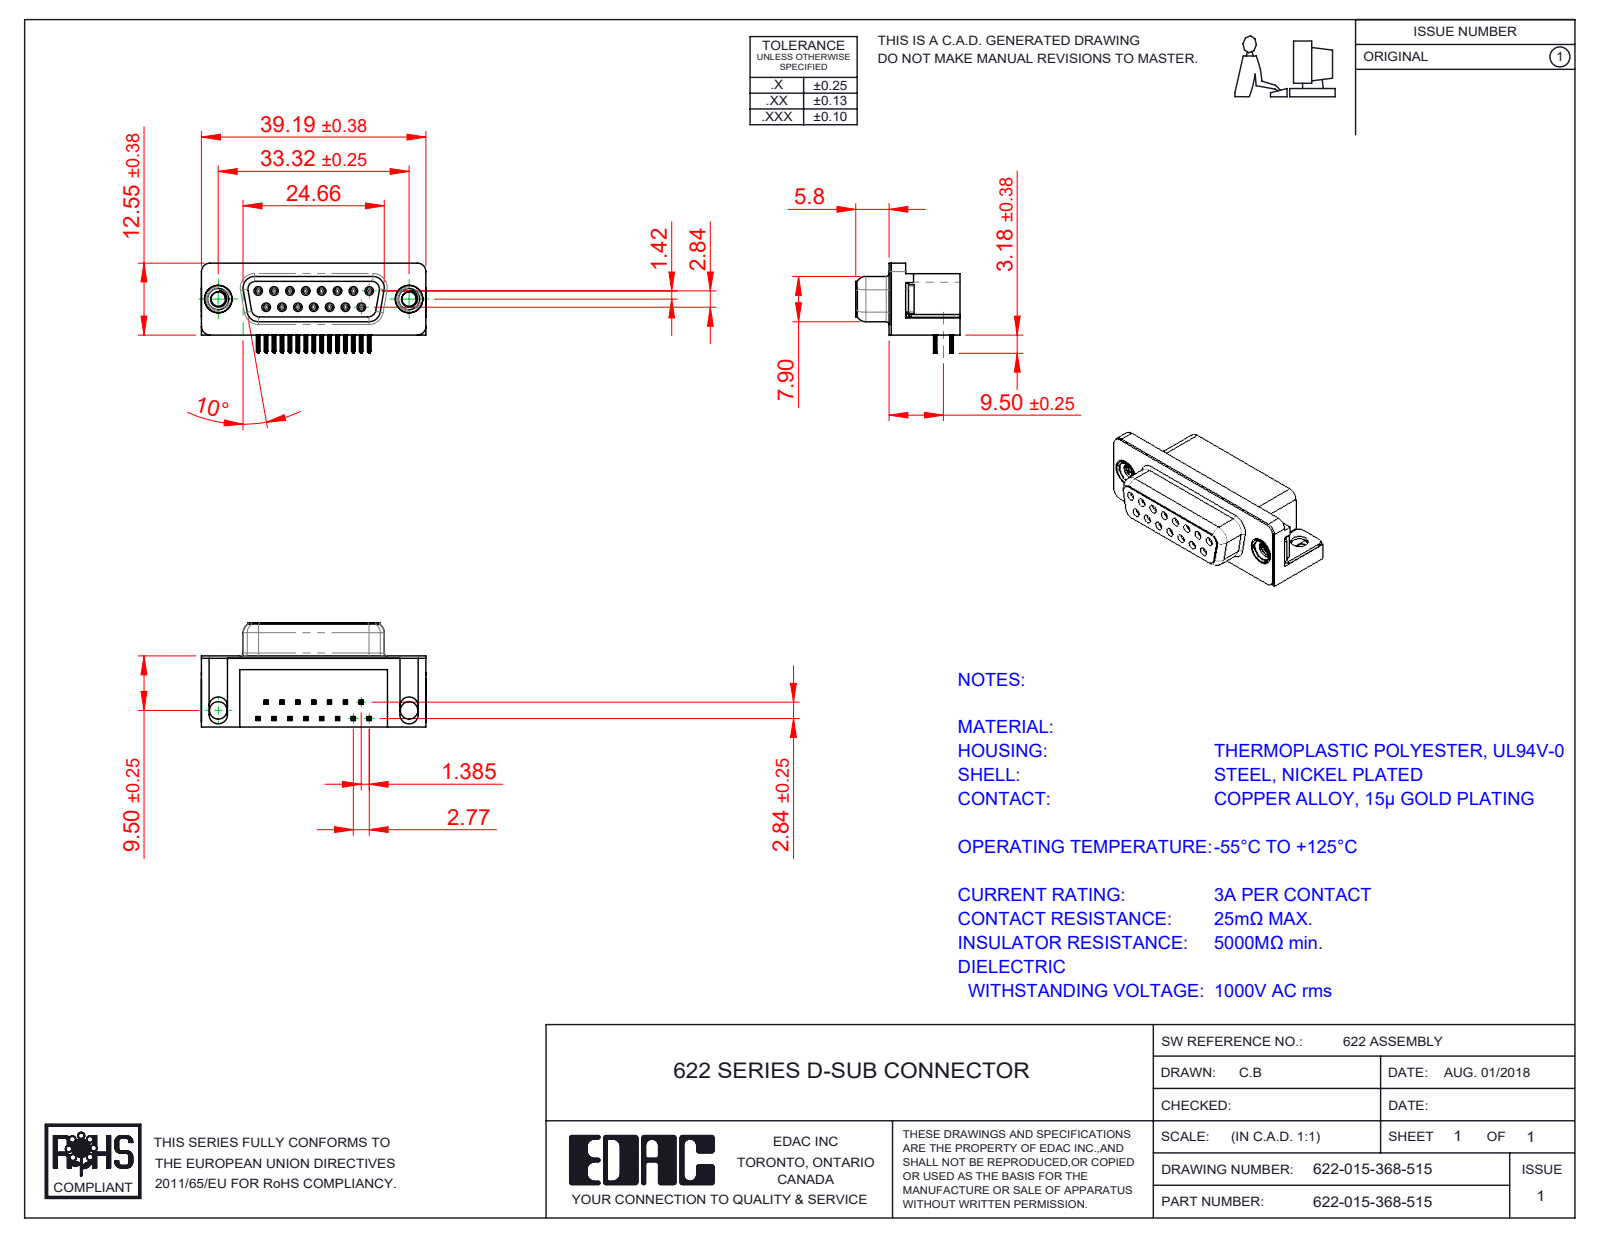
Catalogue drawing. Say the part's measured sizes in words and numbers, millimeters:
The part is named "622-015-368-515; 622 Socket Bottom; 622 Housing_15 Socket; 622 Shell_15 Socket (+3 more)". Its 3-D file was written by "SolidWorks 2016 (CONFIG_CONTROL_DESIGN)". It is 21 solids with 2425 faces: 1072 planar, 609 cylindrical and 744 other. Overall it measures 39.22 by 18.2 by 15.73 millimeters. Its volume is 5 181 cubic millimeters and its surface area 6 706 square millimeters. Round holes: 15 of diameter 0.8, 15 of diameter 0.9, 2 of diameter 2.5, 2 of diameter 3.05, 2 of diameter 4, 2 of diameter 4.8, 2 of diameter 5. Round bosses or shafts: 15 of diameter 1.2, 2 of diameter 4.9, 2 of diameter 4.75, 2 of diameter 3.9. Partial cylindrical surfaces (rounded edges, fillets, slot ends): 120 of radius 0.1, 60 of radius 0.15, 30 of radius 0.35, 18 of radius 1, 15 of radius 0.34, 8 of radius 0.25, 8 of radius 1.35, 8 of radius 1.5. The main face-to-face distances are 0.4, 12, 6.2, 12.4, 10.35, 2.9, 6.65, 0.85, 0.35, 5.8. The hole center spacings are 3.16, 2.77, 5.54, 8.31, 11.08, 5.03, 5.04, 7.48.
